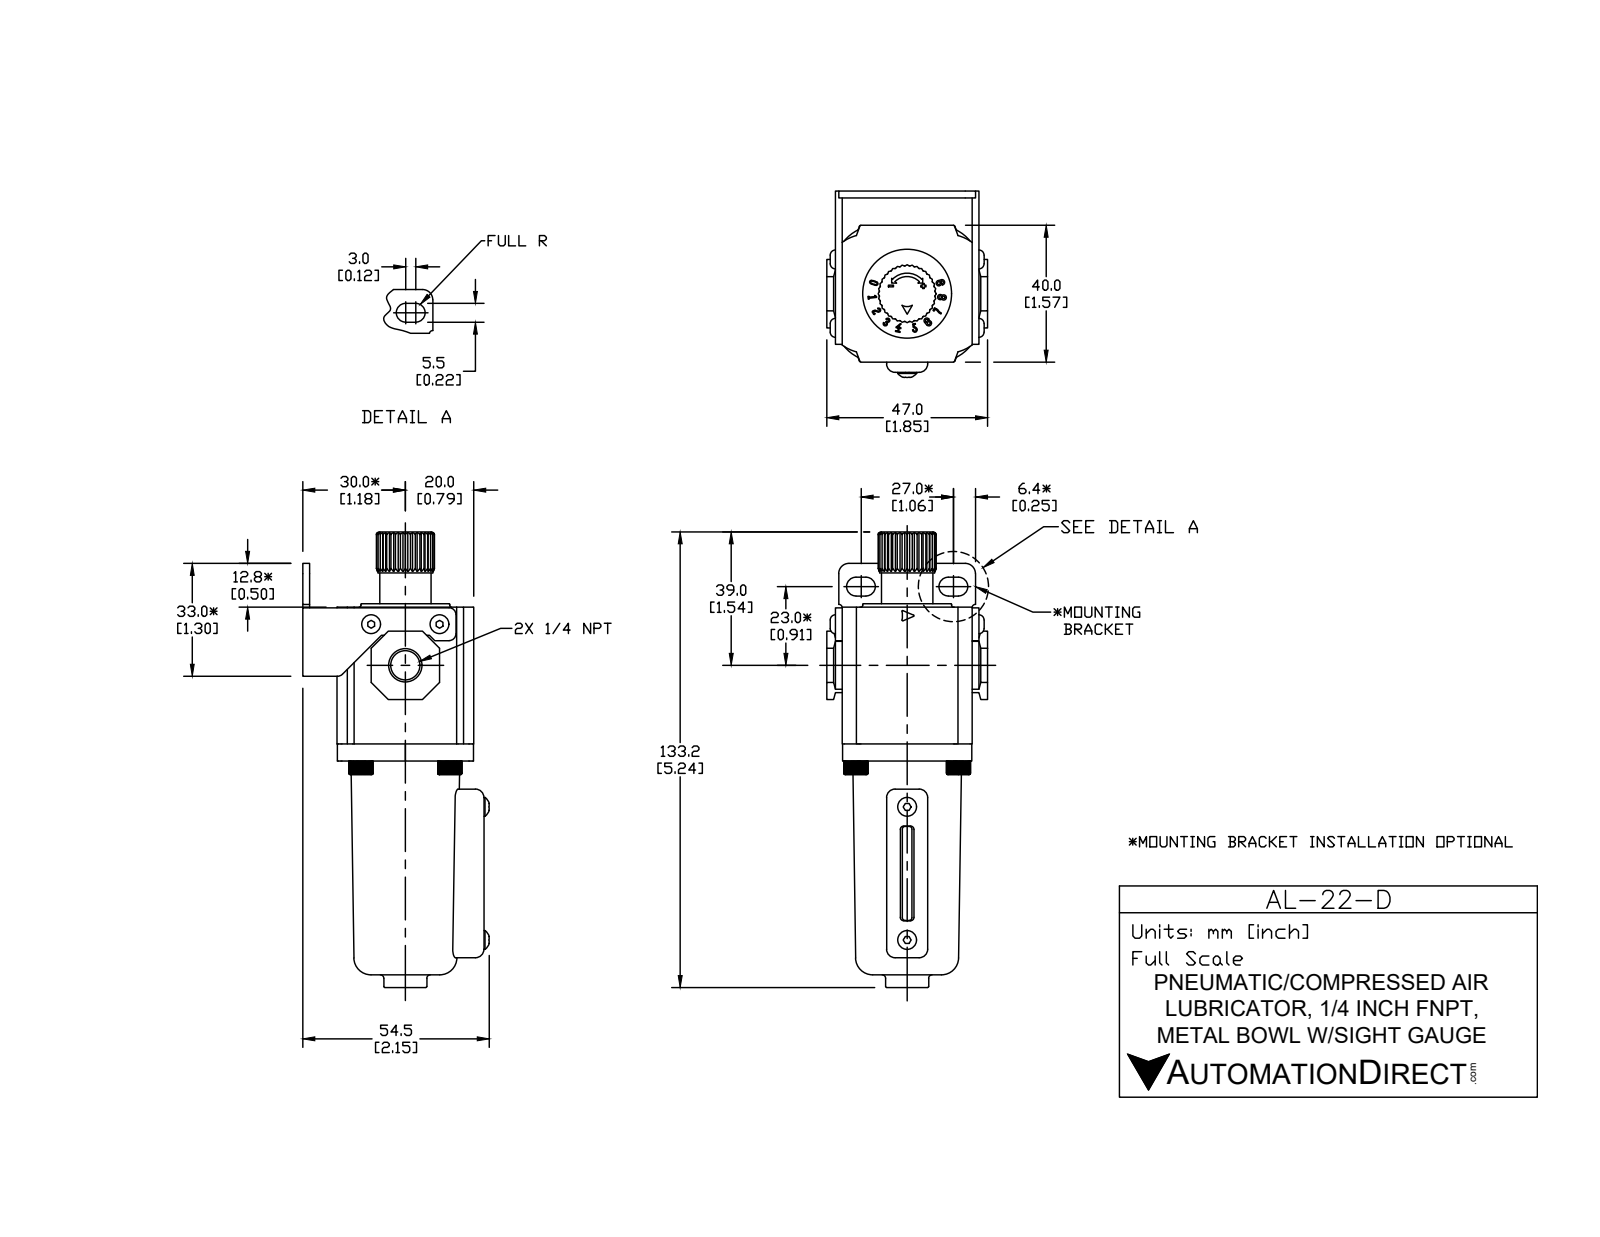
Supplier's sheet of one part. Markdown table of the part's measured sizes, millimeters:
| quantity | value |
| --- | --- |
| part name | AL-22-D |
| STEP written by | SolidWorks 2015 (CONFIG_CONTROL_DESIGN) |
| units | millimeters |
| bodies | 8 solids, 576 faces (326 planar, 122 cylindrical, 128 other) |
| overall size | 133.2 × 55 × 47 |
| volume | 122 301 mm³ |
| surface area | 31 287 mm² |
| round holes (diameter × count) | 3.4 × 2, 11.13 × 1 |
| round bosses / shafts (diameter × count) | 7 × 4, 5.5 × 2, 26 × 1, 15 × 1, 12.6 × 1 |
| partial cylindrical surfaces (radius × count) | 0.3 × 12, 1.3 × 8, 2.5 × 8, 2 × 5, 0.5 × 4, 1 × 4, 2.7 × 4, 11.9 × 4 |
| main face-to-face distances | 40, 2, 38, 8, 10, 50, 48, 1.2, 13, 15 |
| hole center spacings | 15.62, 20 |
